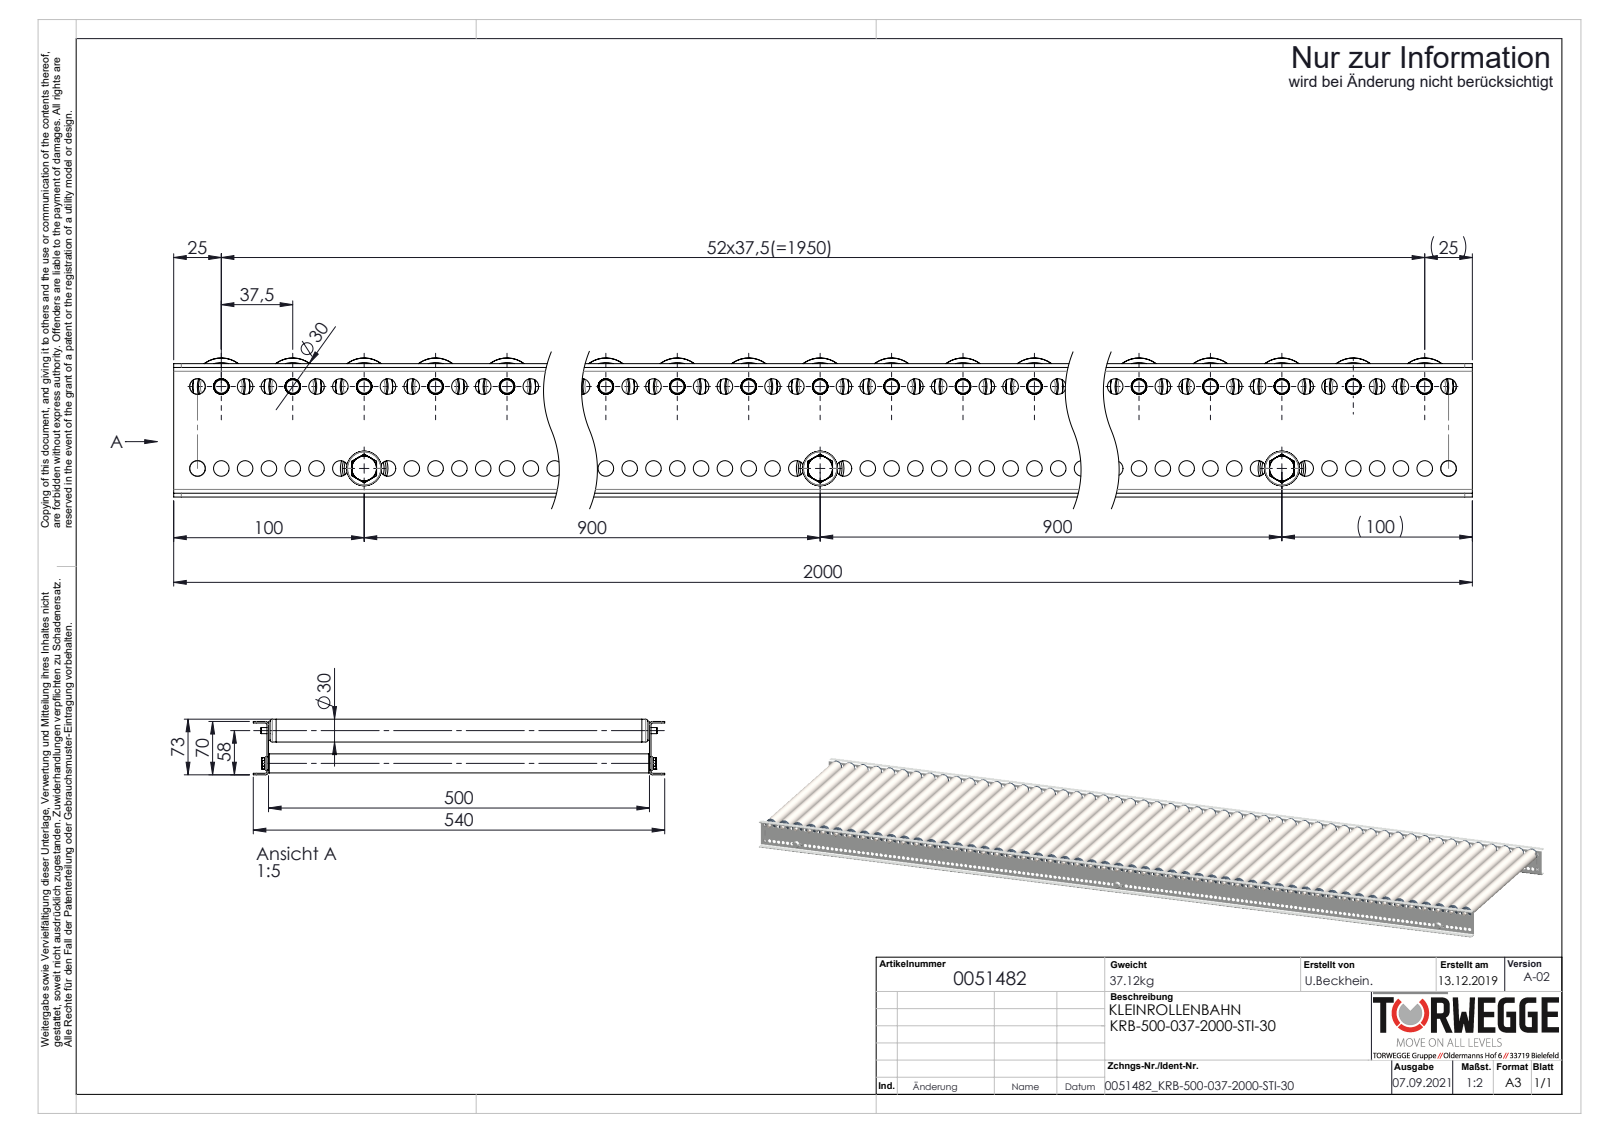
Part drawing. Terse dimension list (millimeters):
name: 0039778-Achse-ST-Ø08-KFG_AL520-G-FA; S100994_Sperrzahnschraube_M08x16-8.8-A2K; 0024176_Passscheibe_DIN988_8x14x1; Traversen_KFG_L500 (+6 more)
written by: SolidWorks 2020 (AUTOMOTIVE_DESIGN)
unit: mm
bodies: 335 solids, 14068 faces (4402 planar, 5588 cylindrical, 4078 other)
size: 2000 × 540 × 73
volume: 5 853 000 mm³; area: 7 059 000 mm²
holes: 318× ⌀8.2, 53× ⌀8, 53× ⌀8.1, 53× ⌀23.2, 53× ⌀25.2, 53× ⌀27, 3× ⌀6.8, 3× ⌀21
bosses: 53× ⌀30, 53× ⌀29.9, 53× ⌀27.1, 53× ⌀26.8, 53× ⌀24, 53× ⌀14, 3× ⌀25, 3× ⌀8
rounds: 53× R5.05, 8× R4, 4× R2
face distances: 2, 502, 500, 68, 504, 70, 66, 10, 490, 20
hole spacings: 12.5, 25, 37.5, 50, 62.5, 75, 87.5, 100
